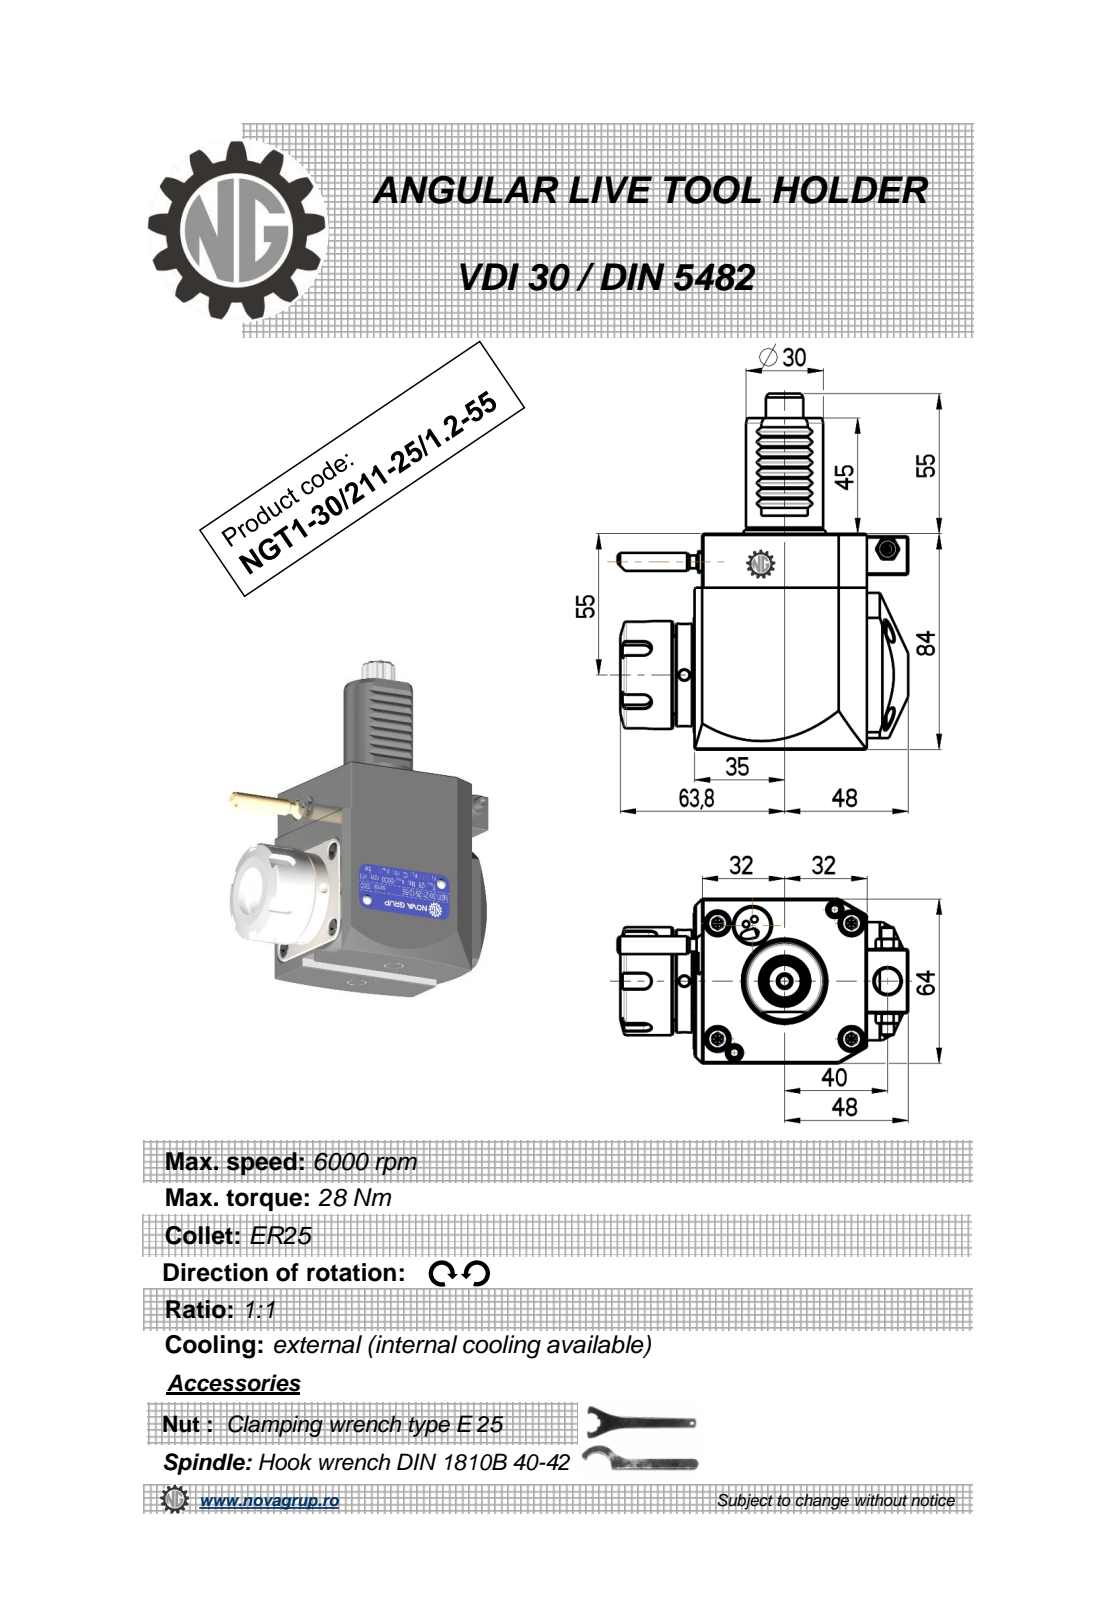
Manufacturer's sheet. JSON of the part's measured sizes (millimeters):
{"part_name": "NGT1_30_211_25_1_2_55", "step_written_by": "PRO/ENGINEER BY PARAMETRIC TECHNOLOGY CORPORATION, 2010280 (CONFIG_CONTROL_DESIGN)", "units": "millimeters", "bodies": {"solids": 1, "faces": 451, "planar": 176, "cylindrical": 118, "other": 157}, "overall_size": [139, 112.88, 65.6], "volume_mm3": 444293, "surface_area_mm2": 45371, "round_holes": [[4, 2], [4.2, 2], [2.5, 1], [3, 1], [9.5, 1], [10, 1], [20.3, 1]], "round_bosses_or_shafts": [[8.96, 2], [5, 2], [42, 1], [40, 1], [33, 1], [30, 1], [7, 1]], "partial_cylinders_radius": [[2.91, 16], [0.26, 12], [0.3, 8], [3, 5], [3.5, 4], [160, 2], [5.7, 1], [7.25, 1]], "face_to_face_distances": [64, 84, 67.2, 3.2, 3, 67, 80, 83, 16, 0.5], "hole_center_spacings": [14.22, 38.95, 40, 46.17, 46.5, 78.95, 92.92]}
